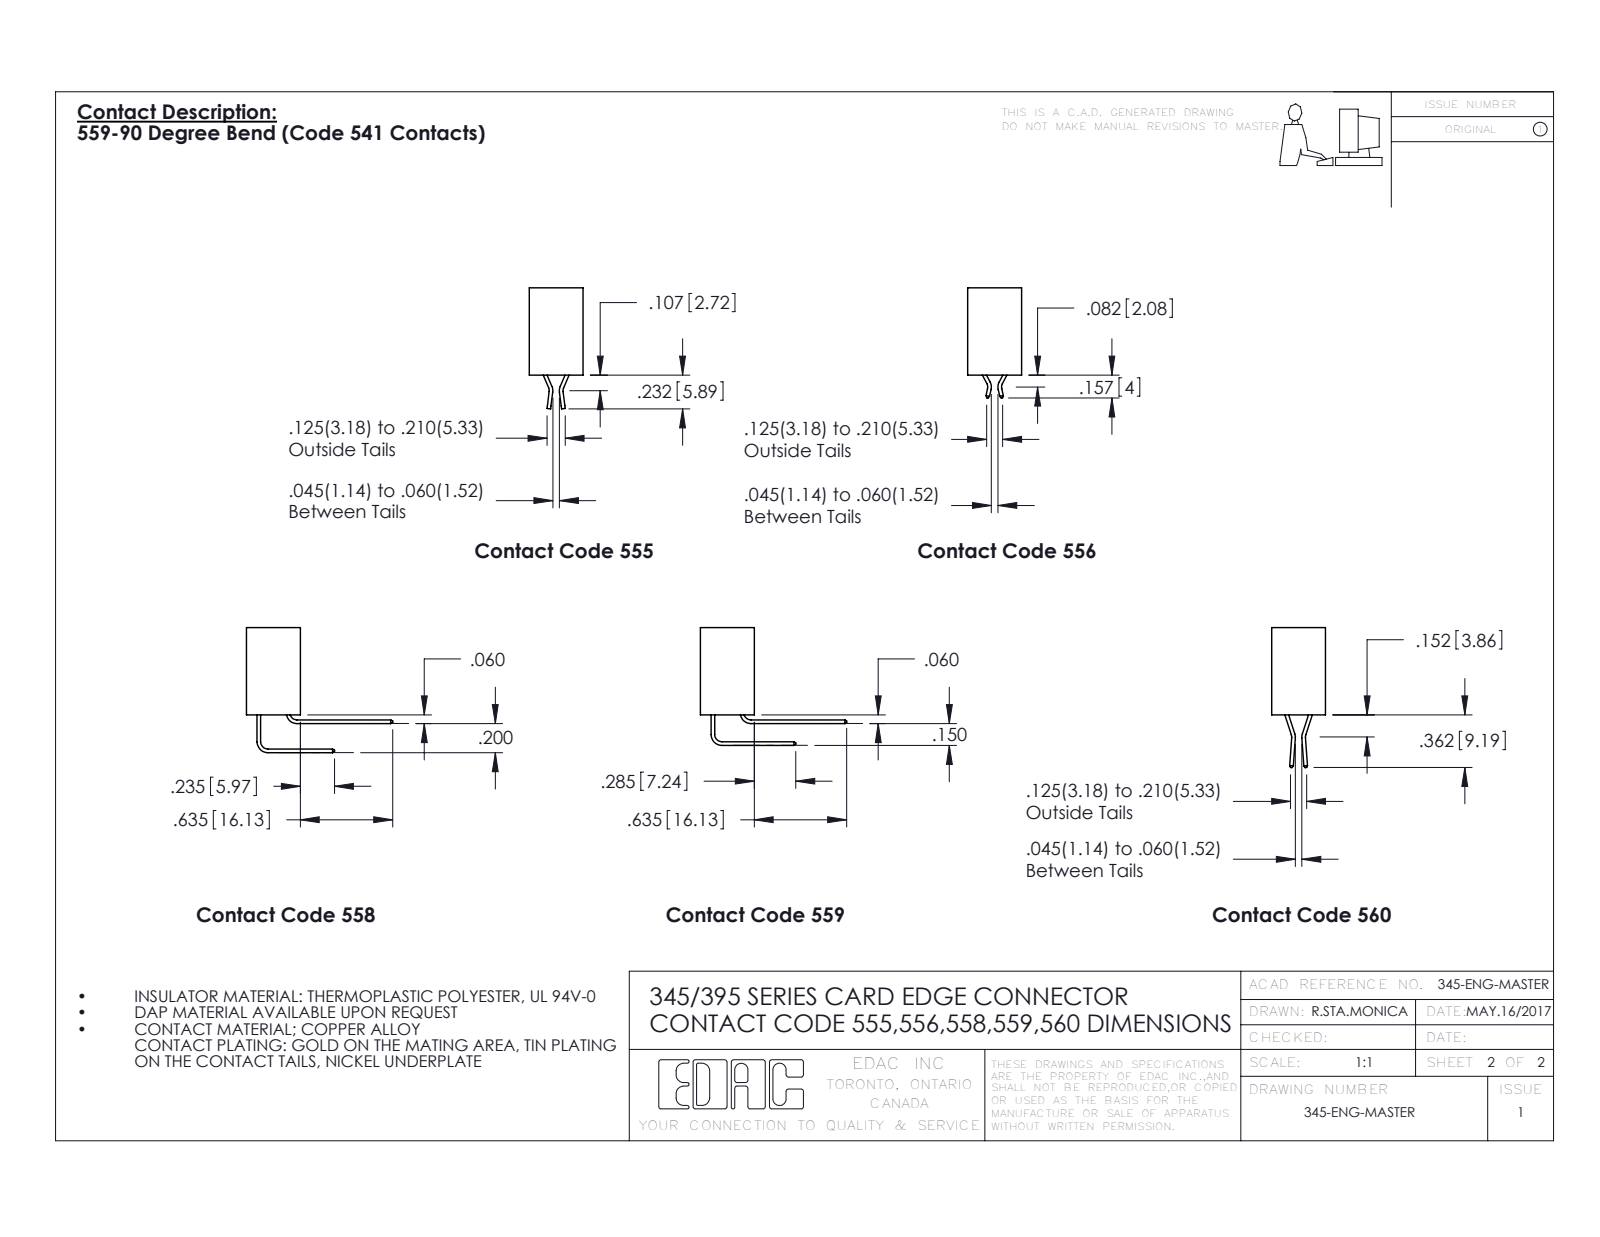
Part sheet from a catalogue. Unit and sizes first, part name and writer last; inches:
Units: inches
Overall size (bounding box): 7.36 × 1.005 × 0.809
Round holes (diameter × count): ⌀0.064 ×1
Partial cylindrical surfaces — rounded edges, fillets, slot ends (radius × count): R0.006 ×283, R0.01 ×22, R0.007 ×6, R0.031 ×6, R0.026 ×3, R0.014 ×2, R0.019 ×2, R0.022 ×2
Main face-to-face distances: 0.072, 0.298, 0.2, 0.37, 0.098, 0.272, 0.025, 0.225, 0.175, 0.15
Volume: 1.212 in³ · Surface area: 52.82 in²
Bodies: 143 solids, 7502 faces (5046 planar, 2456 cylindrical, 0 other)
Part name (STEP PRODUCT): 345-292-001_558 559 Tail - 1; 345 Part_No Mounting Lugs; 395-142-559-201; 345-292-001_559 Tail - 2
STEP written by: SolidWorks 2016 (CONFIG_CONTROL_DESIGN)
